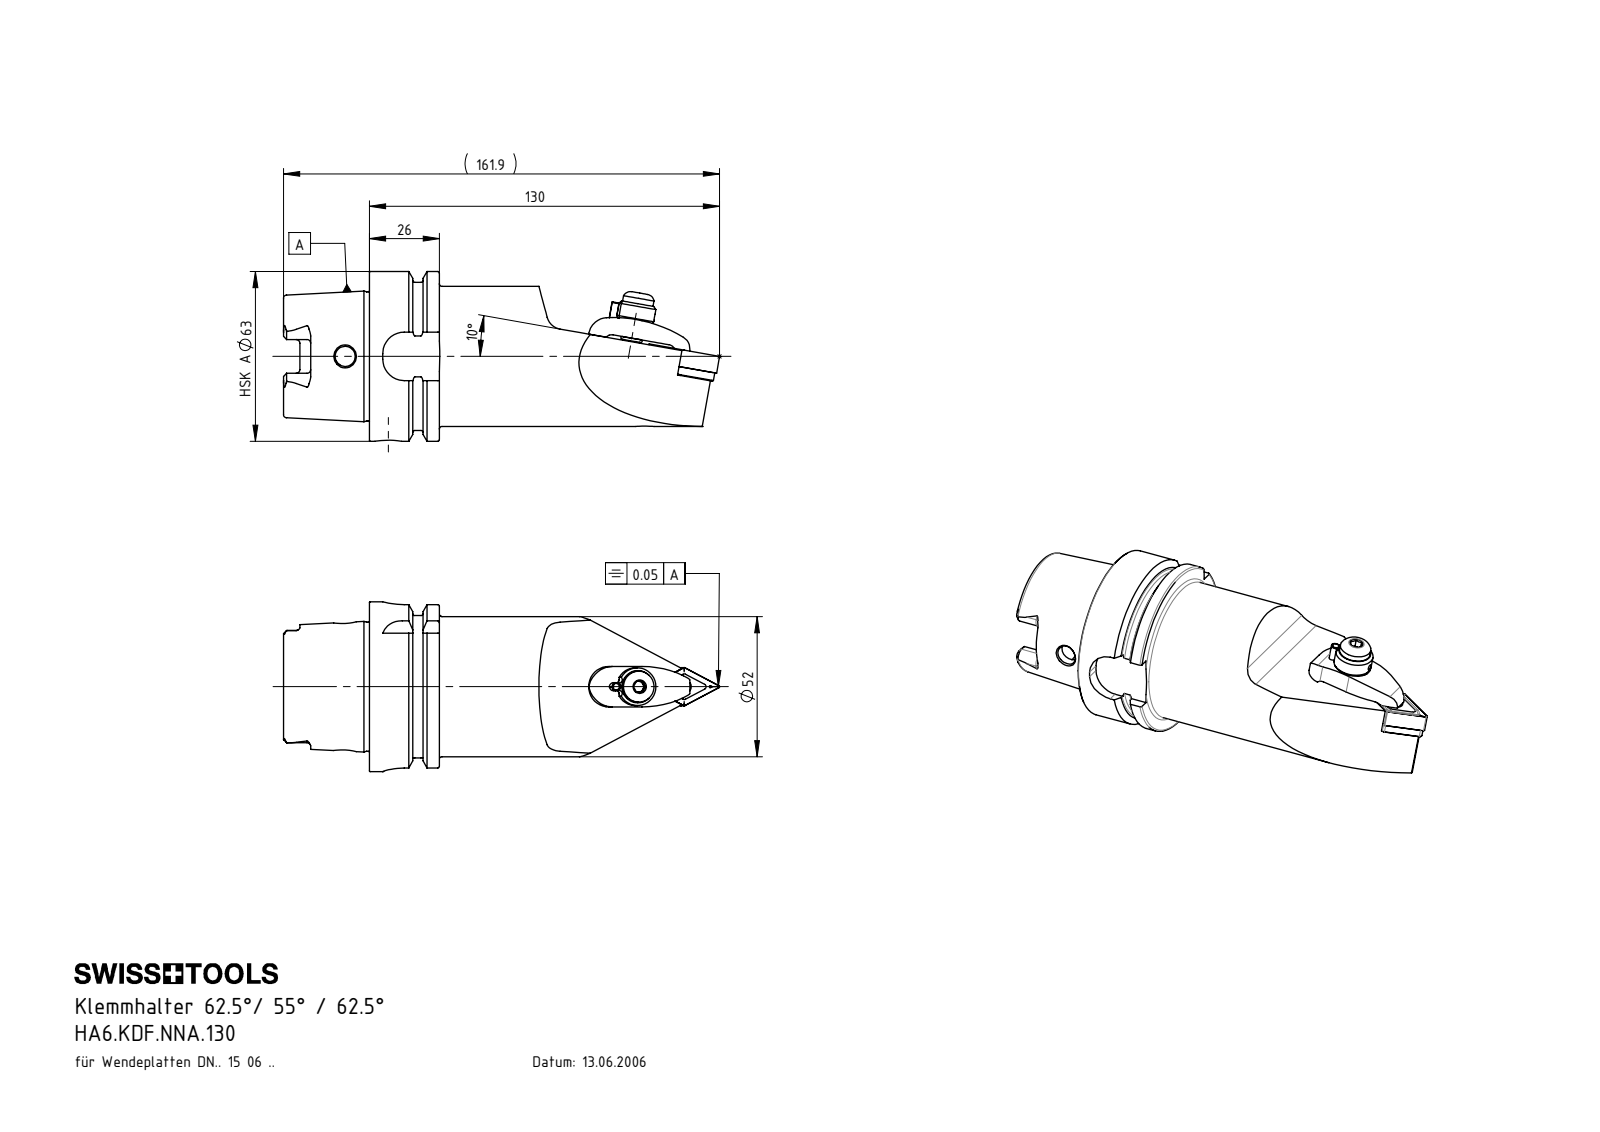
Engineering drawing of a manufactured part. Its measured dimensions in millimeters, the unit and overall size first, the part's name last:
Units: millimetres
Overall size (bounding box): 161.9 × 63 × 63
Round holes (diameter × count): ⌀2 ×3, ⌀5 ×3, ⌀4 ×2, ⌀4.2 ×2, ⌀7 ×2, ⌀2.4 ×1, ⌀3 ×1, ⌀5.16 ×1, ⌀6.2 ×1, ⌀6.4 ×1, ⌀7.5 ×1, ⌀8.4 ×1
Round bosses / shafts (diameter × count): ⌀5 ×2, ⌀3 ×2, ⌀63 ×1, ⌀54.95 ×1, ⌀52 ×1, ⌀47.94 ×1, ⌀14 ×1, ⌀11.5 ×1
Partial cylindrical surfaces — rounded edges, fillets, slot ends (radius × count): R0.39 ×6, R1.4 ×6, R0.4 ×4, R1 ×4, R8 ×4, R0.69 ×3, R0.69 ×3, R1.5 ×3
Main face-to-face distances: 25.95, 16, 9.95, 11.89, 31.9, 41.85, 57.85, 6.05, 52.8, 21.8
Hole centre spacings: 8, 20, 7.99, 8.01, 8.2, 8.21, 19.8, 28
Volume: 228 398 mm³ · Surface area: 42 097 mm²
Bodies: 11 solids, 341 faces (124 planar, 101 cylindrical, 116 other)
Part name (STEP PRODUCT): WCC-ER5.102.005_A; ISO 13337 - 3 x 12_PreviewCfg; DNMG150604; HA6.KDF.NNA.130 (+7 more)
STEP written by: SolidWorks 2017 (AUTOMOTIVE_DESIGN)
